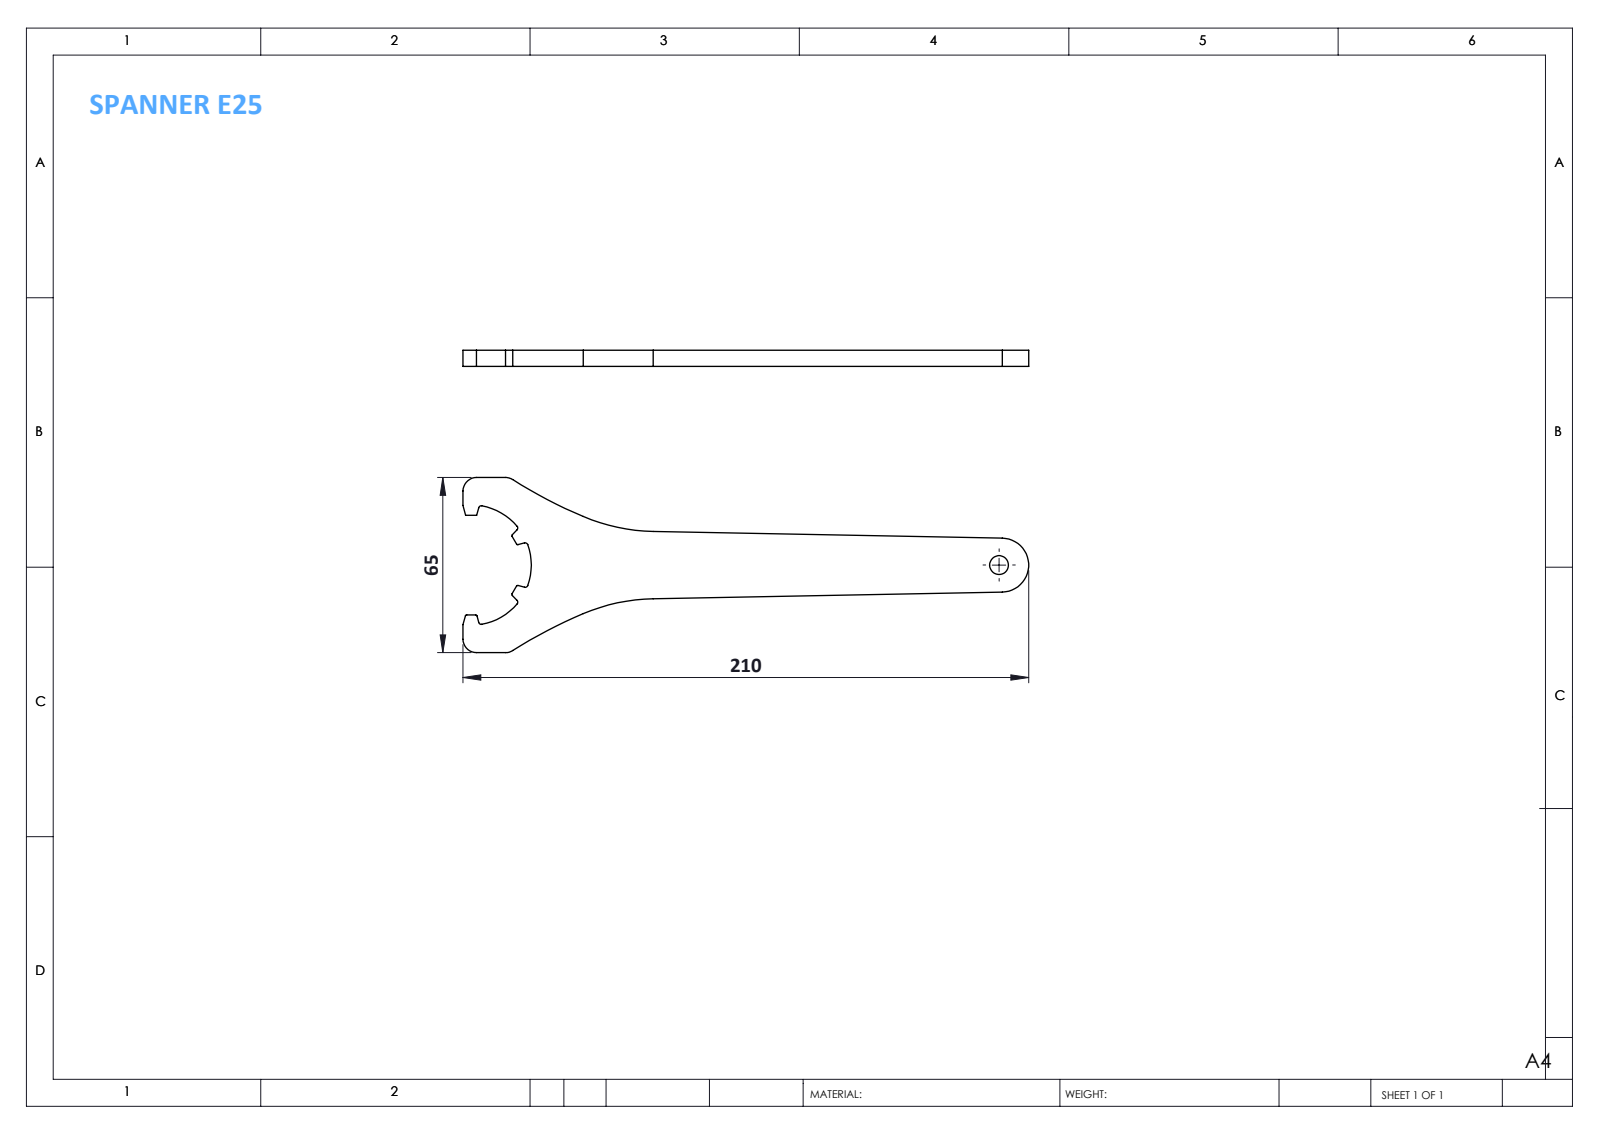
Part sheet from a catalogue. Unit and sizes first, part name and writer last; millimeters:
Units: millimetres
Overall size (bounding box): 210 × 65 × 6
Round holes (diameter × count): ⌀7 ×1
Partial cylindrical surfaces — rounded edges, fillets, slot ends (radius × count): R0.5 ×6, R1 ×6, R5 ×4, R70.11 ×2, R181.24 ×2, R10 ×1, R22.33 ×1
Main face-to-face distances: 6, 65, 14, 51, 5.62, 37
Volume: 32 408 mm³ · Surface area: 14 248 mm²
Bodies: 1 solid, 50 faces (20 planar, 30 cylindrical, 0 other)
Part name (STEP PRODUCT): SPANNER E25
STEP written by: SolidWorks 2014 (CONFIG_CONTROL_DESIGN)
